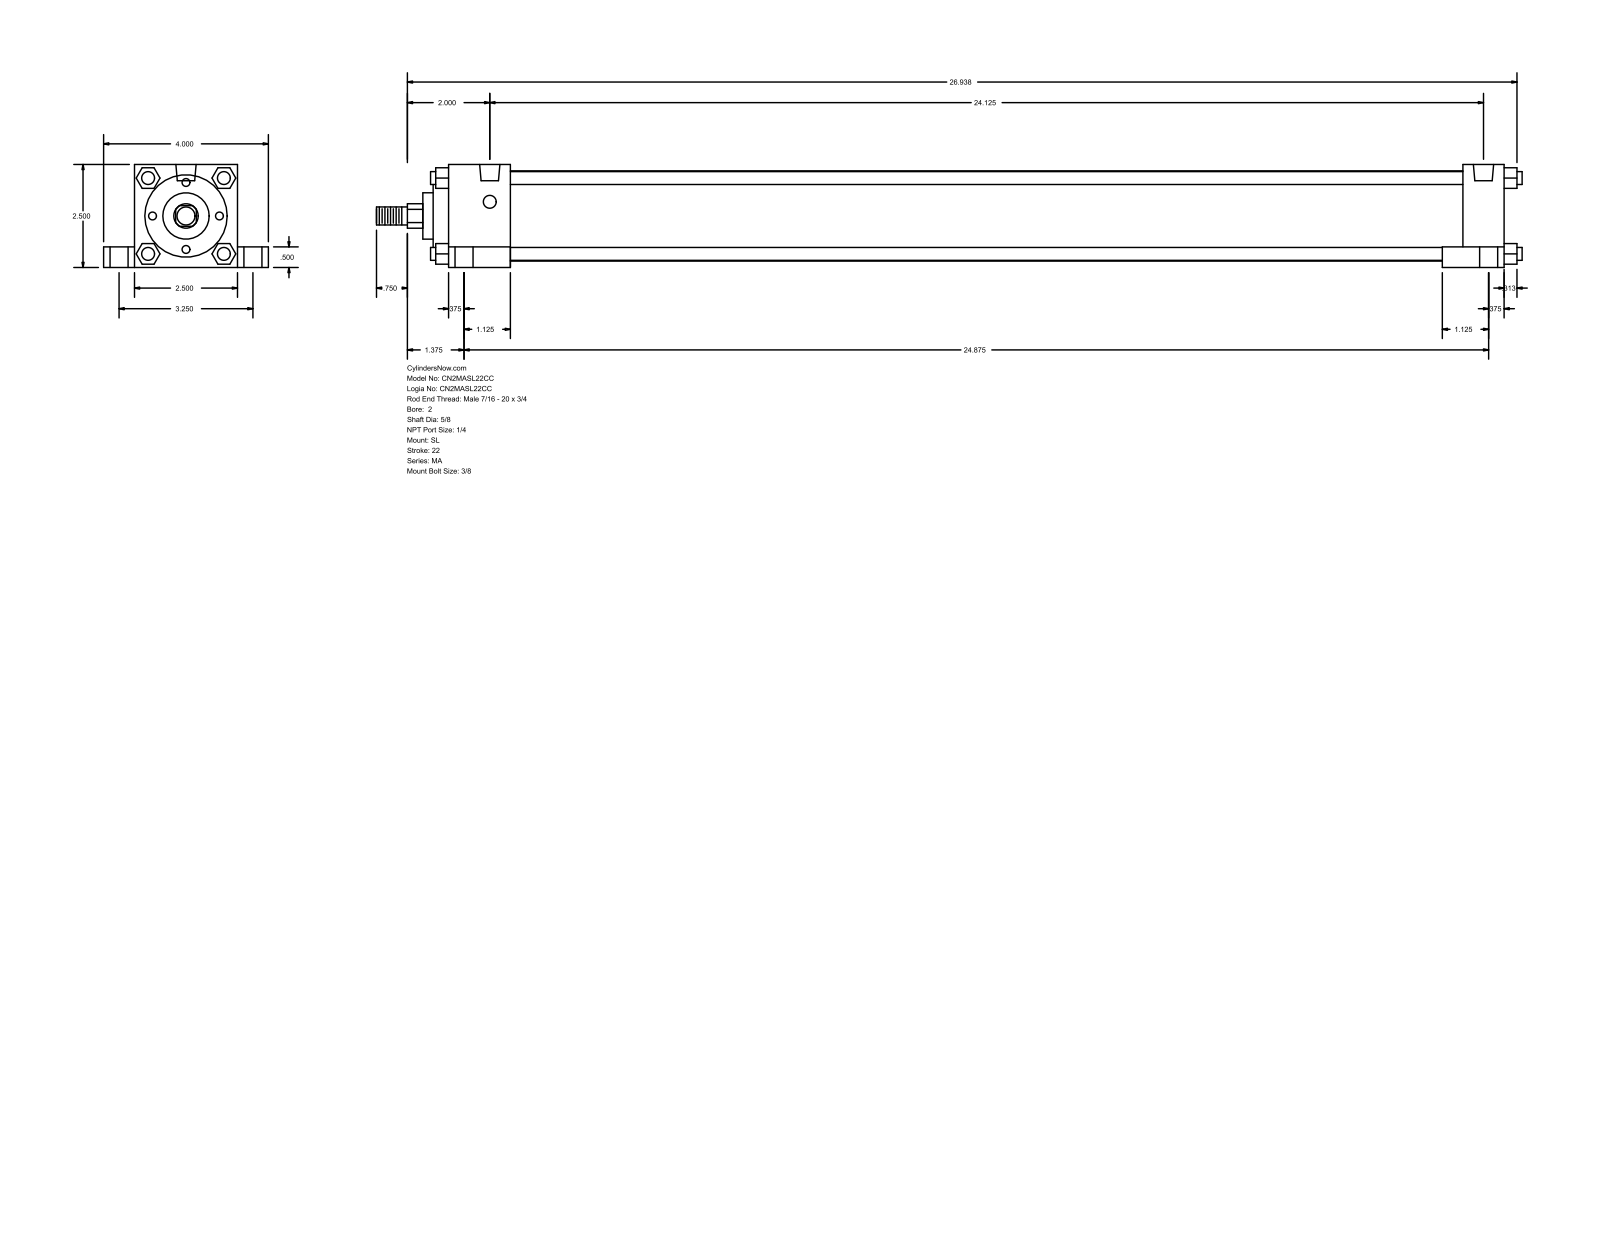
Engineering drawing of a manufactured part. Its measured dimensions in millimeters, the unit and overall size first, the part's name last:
Units: millimetres
Overall size (bounding box): 706.44 × 101.6 × 63.5
Round holes (diameter × count): ⌀7.94 ×4, ⌀11.11 ×4, ⌀17.46 ×4, ⌀12.49 ×2
Round bosses / shafts (diameter × count): ⌀7.94 ×4, ⌀55.63 ×1, ⌀50.8 ×1, ⌀28.57 ×1, ⌀15.88 ×1, ⌀11.11 ×1
Partial cylindrical surfaces — rounded edges, fillets, slot ends (radius × count): R7.54 ×1
Main face-to-face distances: 63.5, 12.7, 9.52, 19.05, 82.55, 38.1, 50.8, 650.87, 612.77, 625.48
Hole centre spacings: 41.39, 44.22, 82.54, 612.78, 617.33, 630.01, 631.83, 637.2
Bodies: 0 solids, 150 faces (113 planar, 37 cylindrical, 0 other)
Part name (STEP PRODUCT): MA_SL__0200_0.625
STEP written by: GSSL Pune (CONFIG_CONTROL_DESIGN)
